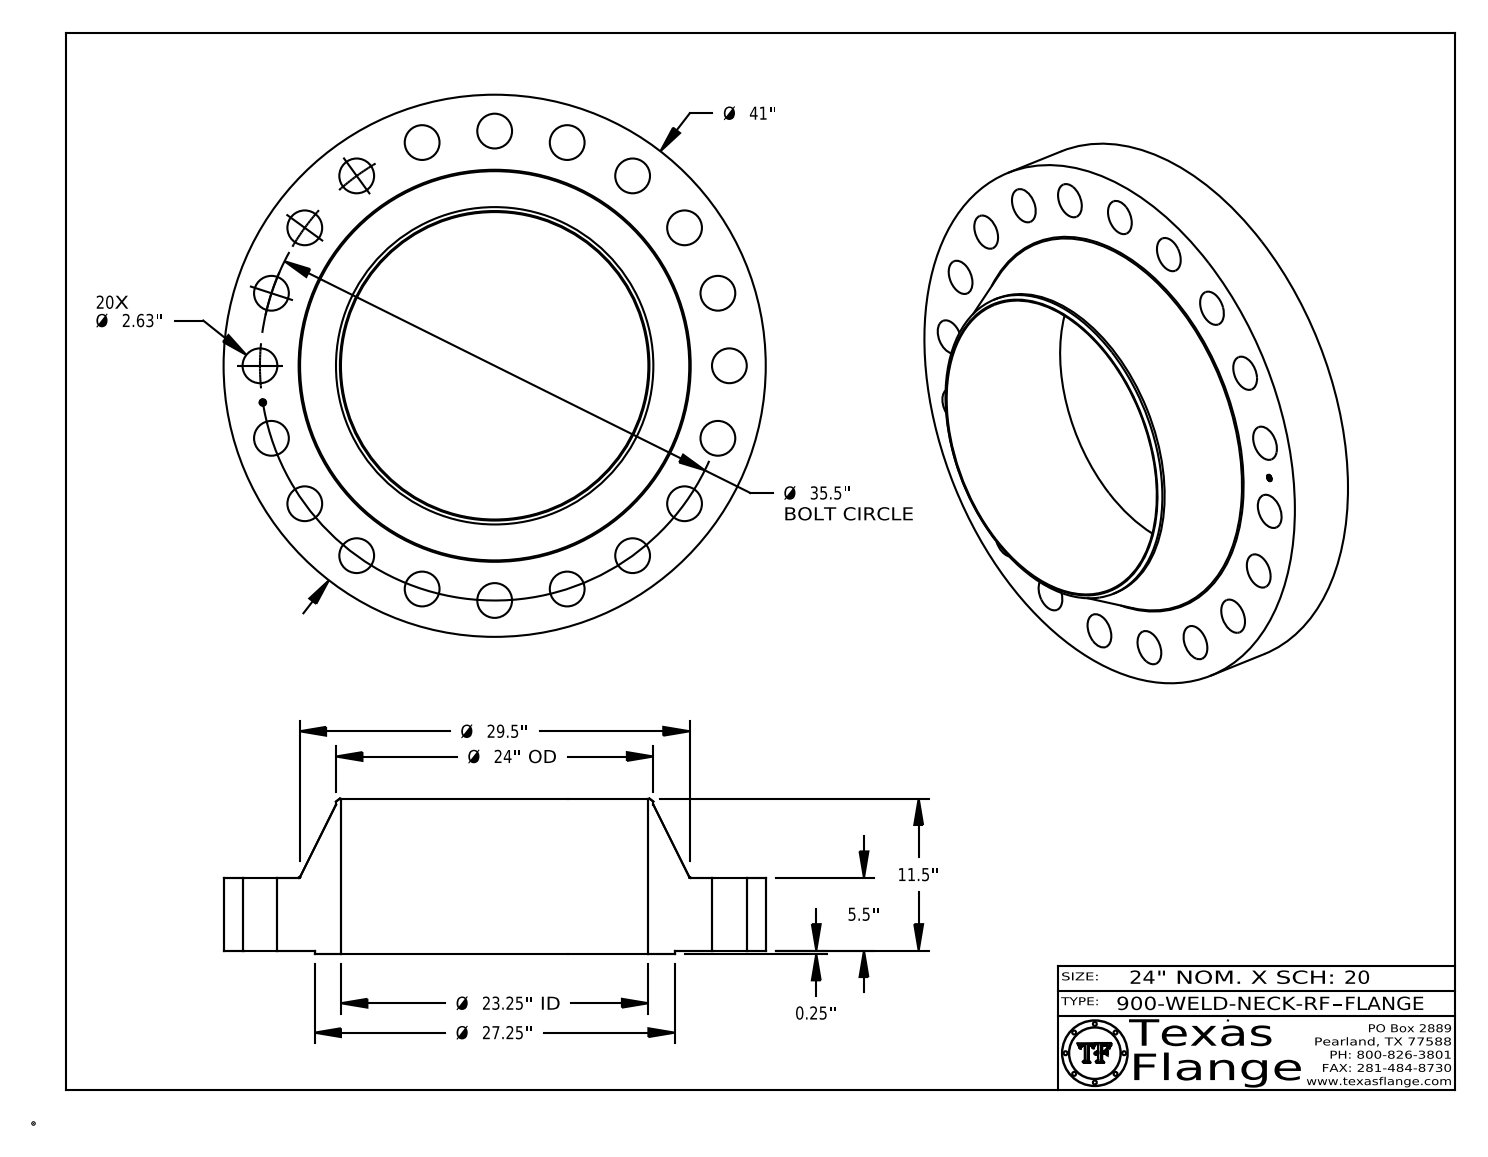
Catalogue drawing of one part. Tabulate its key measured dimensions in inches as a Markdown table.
| quantity | value |
| --- | --- |
| part name | 900-WELD-NECK-RF |
| STEP written by | CATIA V5 STEP AP214 (AUTOMOTIVE_DESIGN) |
| units | inches |
| bodies | 1 solid, 443 faces (369 planar, 68 cylindrical, 6 other) |
| overall size | 41 × 41 × 11.75 |
| volume | 5 151 in³ |
| surface area | 4 382 in² |
| round holes (diameter × count) | 2.63 × 20, 0.495 × 1, 23.25 × 1 |
| round bosses / shafts (diameter × count) | 0.03 × 8, 41 × 1, 27.25 × 1, 24 × 1, 0.39 × 1 |
| main face-to-face distances | 5.5, 0.25, 5.75, 11.75, 11.5, 6, 5.735, 5.485, 0.015, 6.015 |
| hole center spacings | 17.75, 10.97, 28.72, 31.631, 16.117, 20.866, 25.102, 33.762 |
